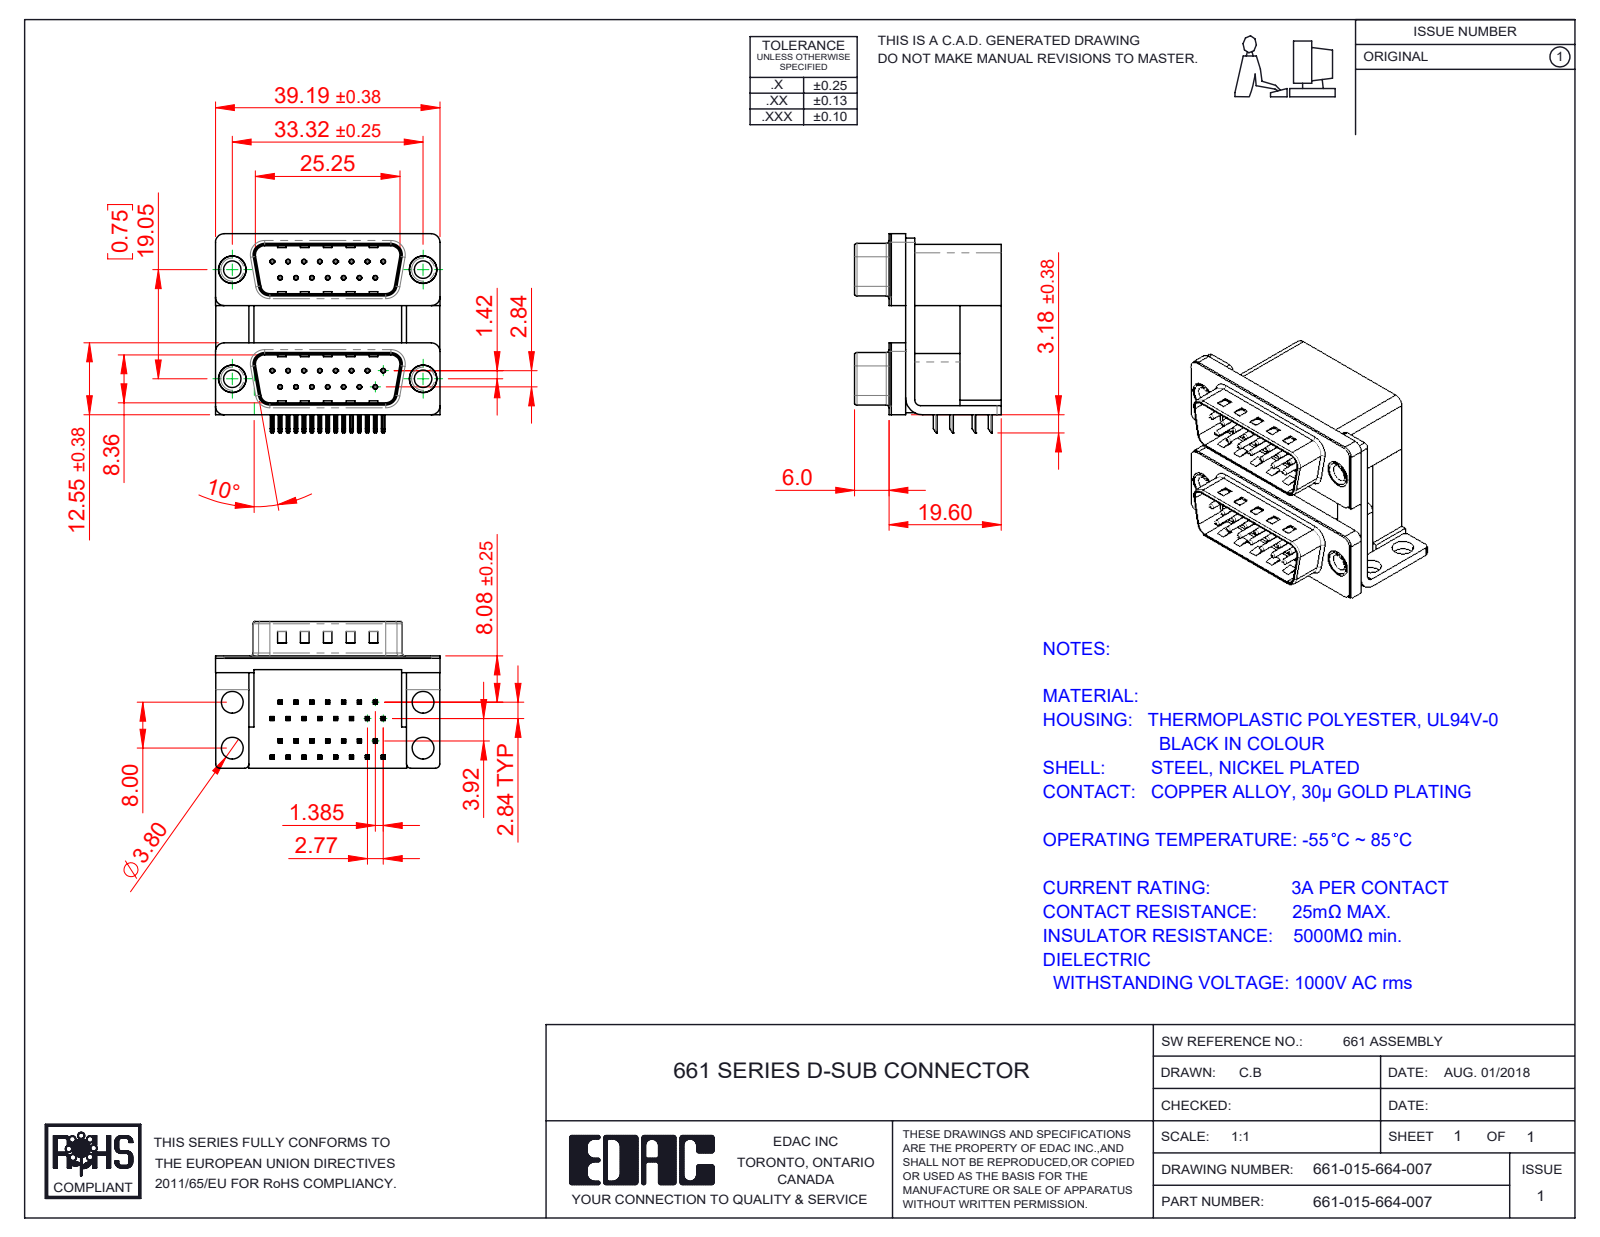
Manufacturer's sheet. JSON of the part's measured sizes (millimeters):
{"part_name": "661 Contact Bottom Lower; 661 Contact Top Lower; 661-015-664-007; 661 Thru Hole Rivet (+7 more)", "step_written_by": "SolidWorks 2020 (CONFIG_CONTROL_DESIGN)", "units": "millimeters", "bodies": {"solids": 41, "faces": 2878, "planar": 1834, "cylindrical": 818, "other": 226}, "overall_size": [39.19, 34.78, 25.6], "volume_mm3": 14345, "surface_area_mm2": 15566, "round_holes": [[0.35, 30], [0.8, 30], [3.05, 4], [3.5, 4], [3.8, 4], [4, 4], [4.8, 4], [5, 4]], "round_bosses_or_shafts": [[0.75, 30], [4.9, 4], [4.75, 4], [3.85, 4]], "partial_cylinders_radius": [[0.25, 120], [0.12, 60], [0.5, 16], [1.5, 16], [0.75, 8], [0.9, 8], [1.6, 8], [2, 8]], "face_to_face_distances": [0.4, 19.05, 19.2, 10.69, 16.7, 2.5, 7.2, 12, 9.5, 1.6], "hole_center_spacings": [3.16, 2.77, 19.25, 5.54, 19.84, 8.31, 20.78, 19.05]}
